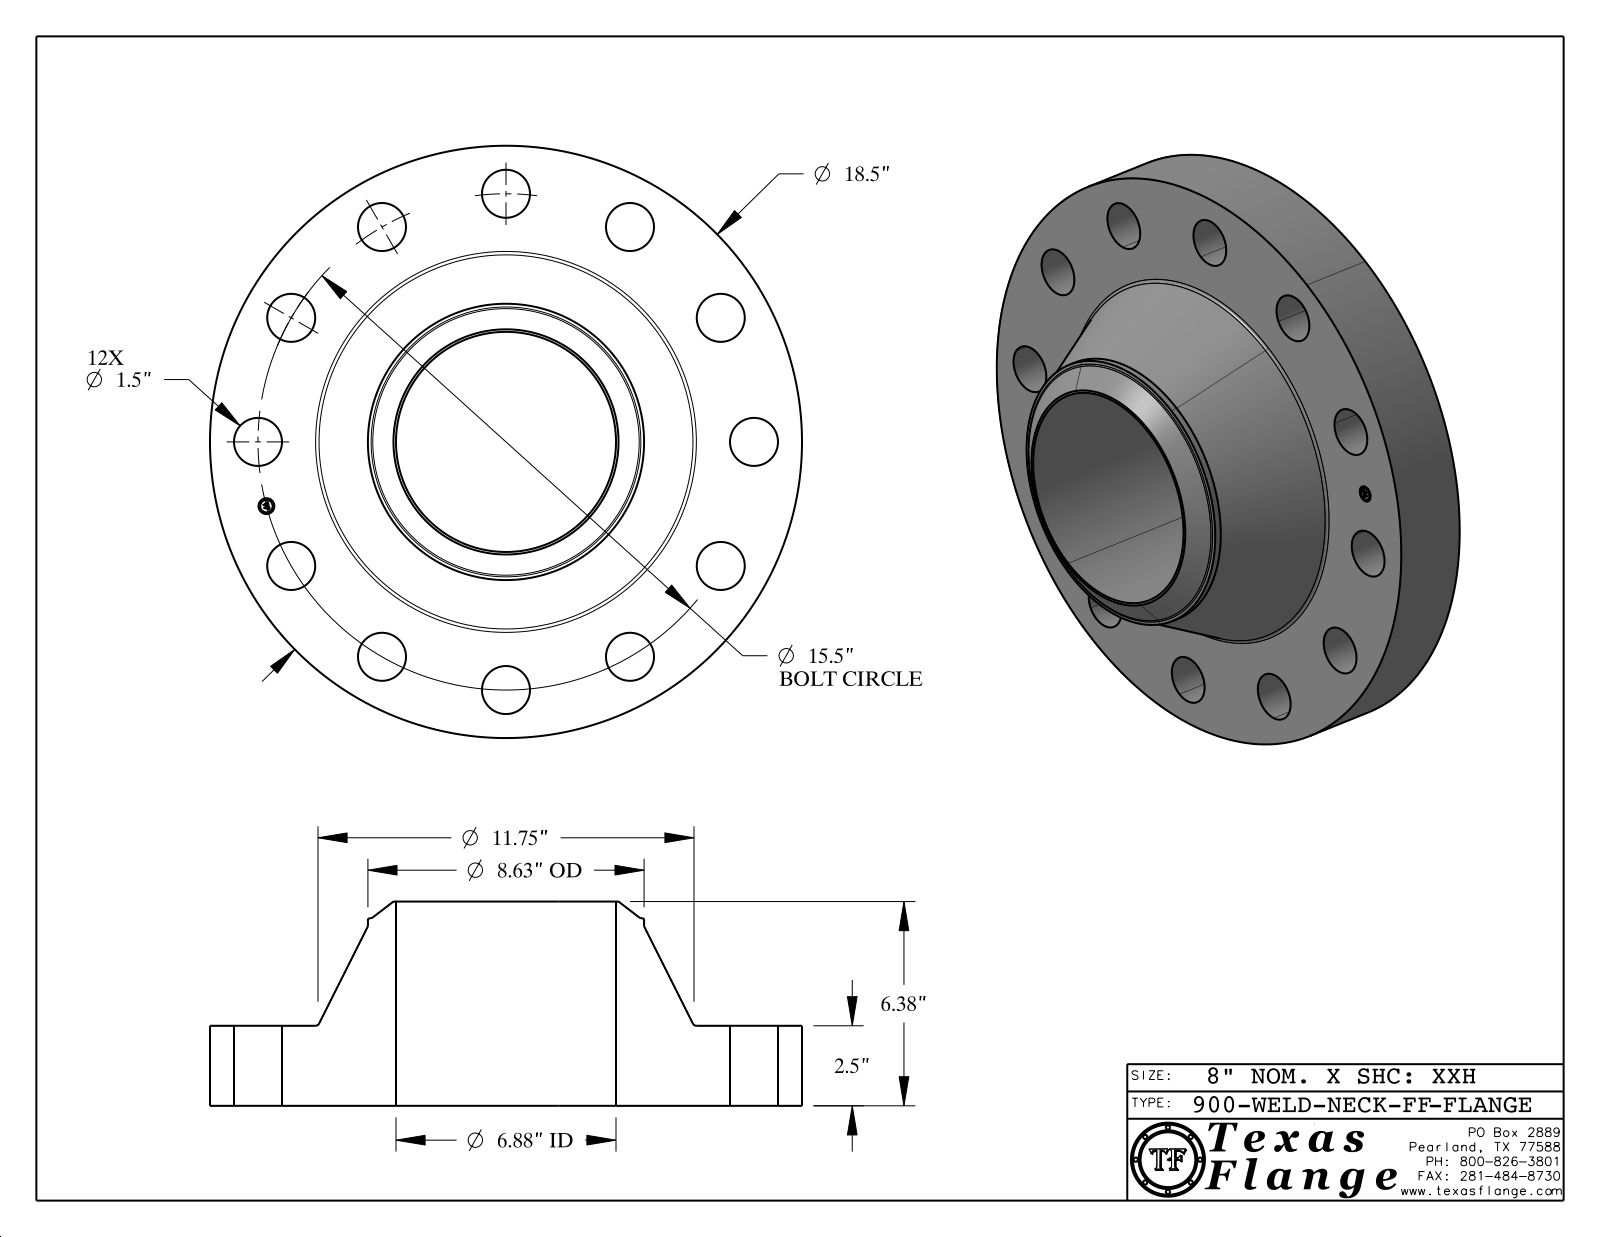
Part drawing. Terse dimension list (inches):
name: 900-WELD-NECK-FF
written by: CATIA V5 STEP AP214 (AUTOMOTIVE_DESIGN)
unit: in
bodies: 1 solid, 428 faces (368 planar, 50 cylindrical, 10 other)
size: 18.5 × 18.5 × 6.38
volume: 676.7 in³; area: 917 in²
holes: 12× ⌀1.5, 1× ⌀0.495, 1× ⌀6.875
bosses: 8× ⌀0.03, 1× ⌀18.5, 1× ⌀8.63, 1× ⌀0.39
face distances: 2.5, 6.38, 3.88, 0.015, 2.485, 3.895, 0.148, 0.145, 0.027, 0.096
hole spacings: 7.75, 7.75, 13.424, 4.012, 10.961, 14.972, 4.011, 10.96
